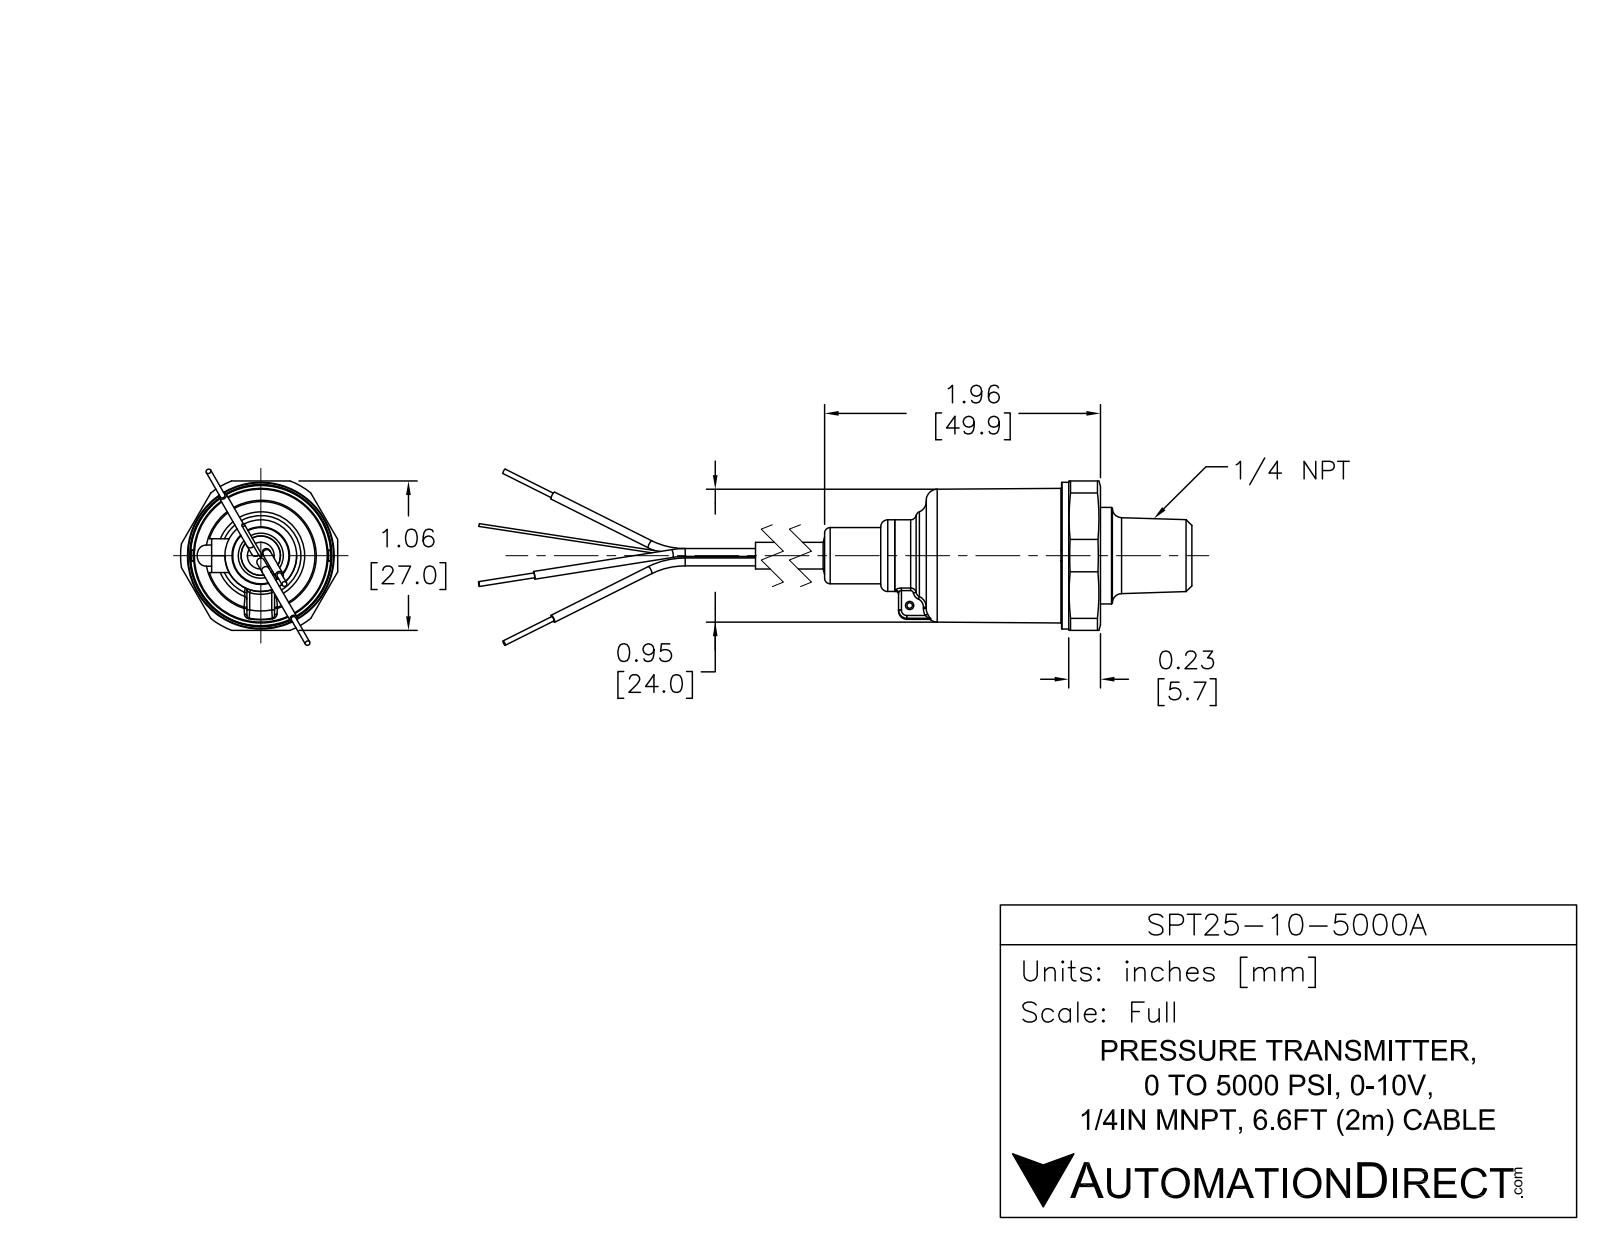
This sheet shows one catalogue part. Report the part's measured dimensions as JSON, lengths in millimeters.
{"part_name": "SPT25-10-5000A", "step_written_by": "SolidWorks 2017 (AUTOMOTIVE_DESIGN)", "units": "millimeters", "bodies": {"solids": 7, "faces": 116, "planar": 32, "cylindrical": 49, "other": 35}, "overall_size": [153.3, 29, 27.09], "volume_mm3": 20801, "surface_area_mm2": 7170, "round_holes": [[1, 1], [3.3, 1]], "round_bosses_or_shafts": [[1.4, 6], [0.75, 5], [26.75, 1], [24, 1], [17.5, 1], [14, 1], [13, 1], [10, 1]], "partial_cylinders_radius": [[2, 1], [14.5, 1]], "face_to_face_distances": [6.75, 24, 17.25, 42.75, 49.5, 66.75, 44, 1.25, 5.5, 22.75]}
